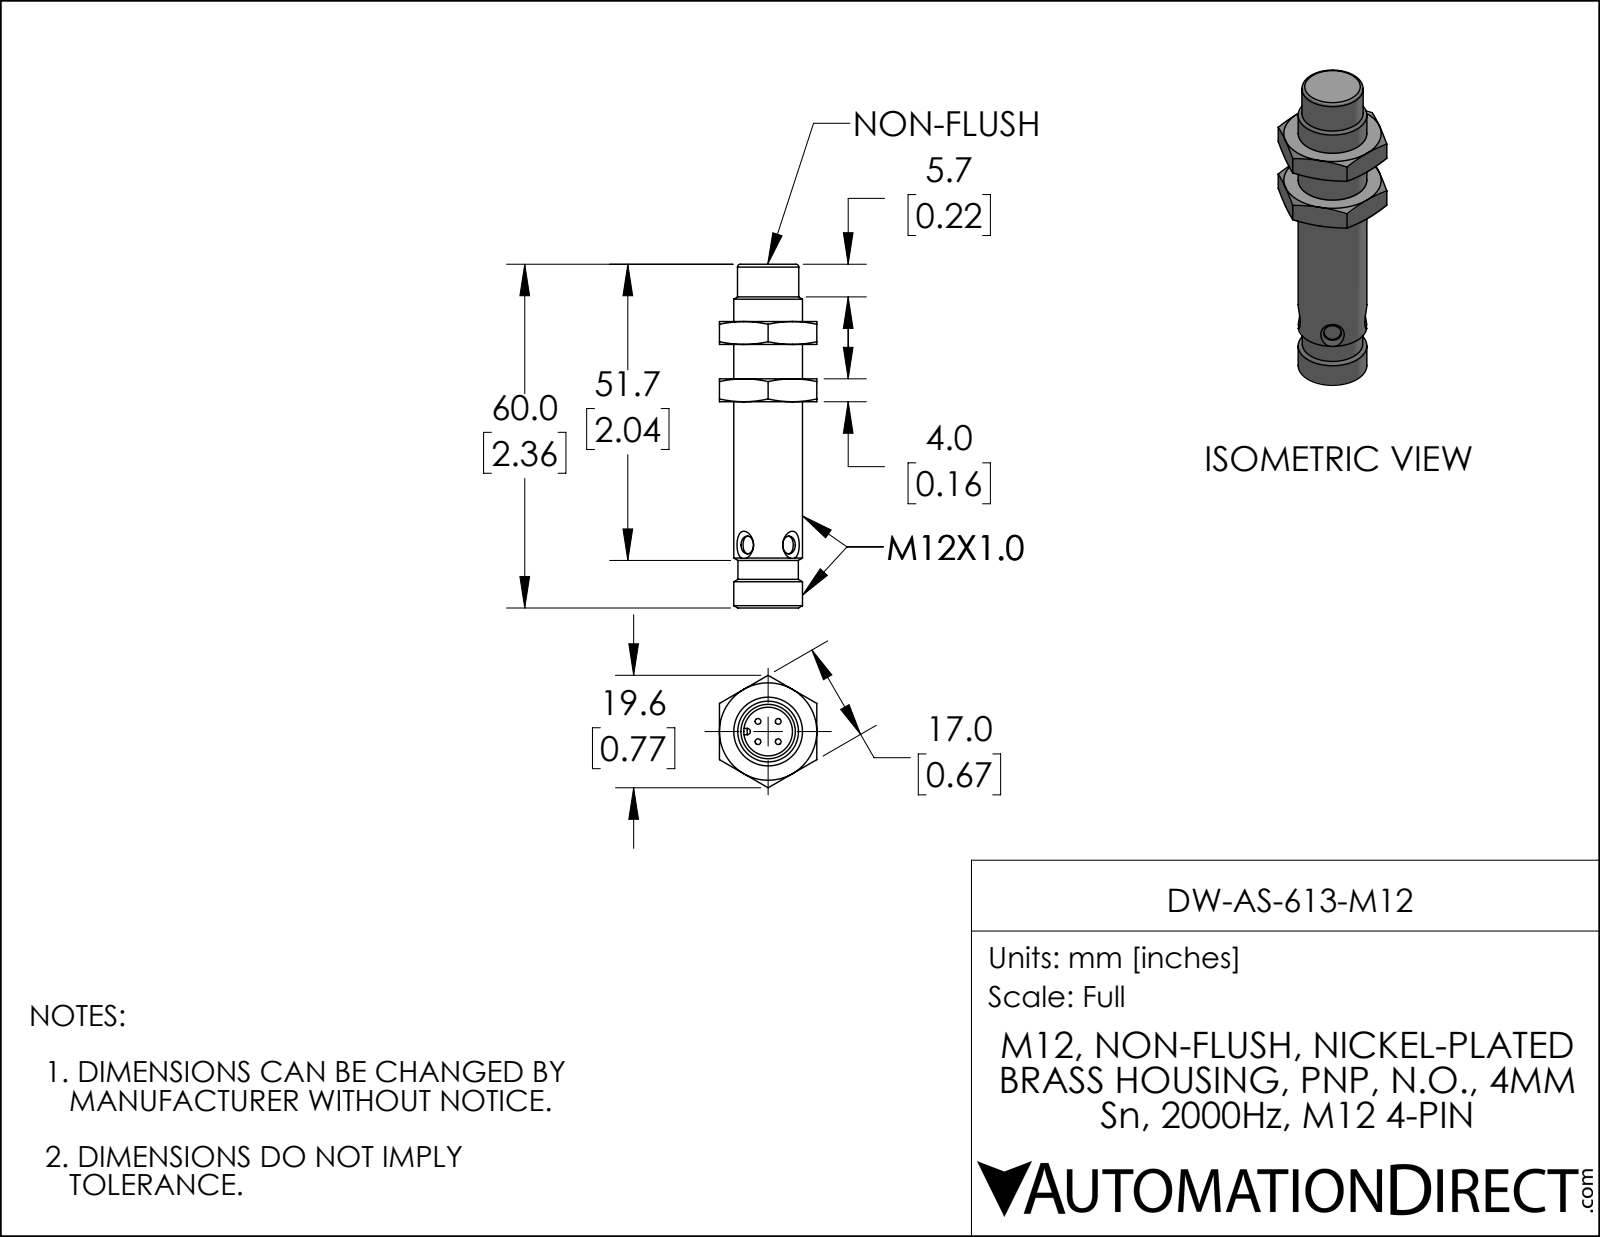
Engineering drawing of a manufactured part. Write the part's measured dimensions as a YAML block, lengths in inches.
part_name: "DW-AS-613-M12"
step_written_by: "SolidWorks 2019 (AUTOMOTIVE_DESIGN)"
units: inches
bodies: {solids: 1, faces: 82, planar: 22, cylindrical: 21, other: 39}
overall_size: [2.362, 0.773, 0.669]
volume: 0.434
surface_area: 5.407
round_holes:
  - {diameter: 0.122, count: 2}
  - {diameter: 0.335, count: 1}
round_bosses_or_shafts:
  - {diameter: 0.039, count: 4}
  - {diameter: 0.472, count: 1}
  - {diameter: 0.421, count: 1}
  - {diameter: 0.415, count: 1}
partial_cylinders:
  - {radius: 0.022, count: 2}
  - {radius: 0.193, count: 1}
face_to_face_distances: [0.394, 0.157, 0.669, 0.551, 0.236, 0.787, 0.945, 2.02, 1.626, 1.469]
